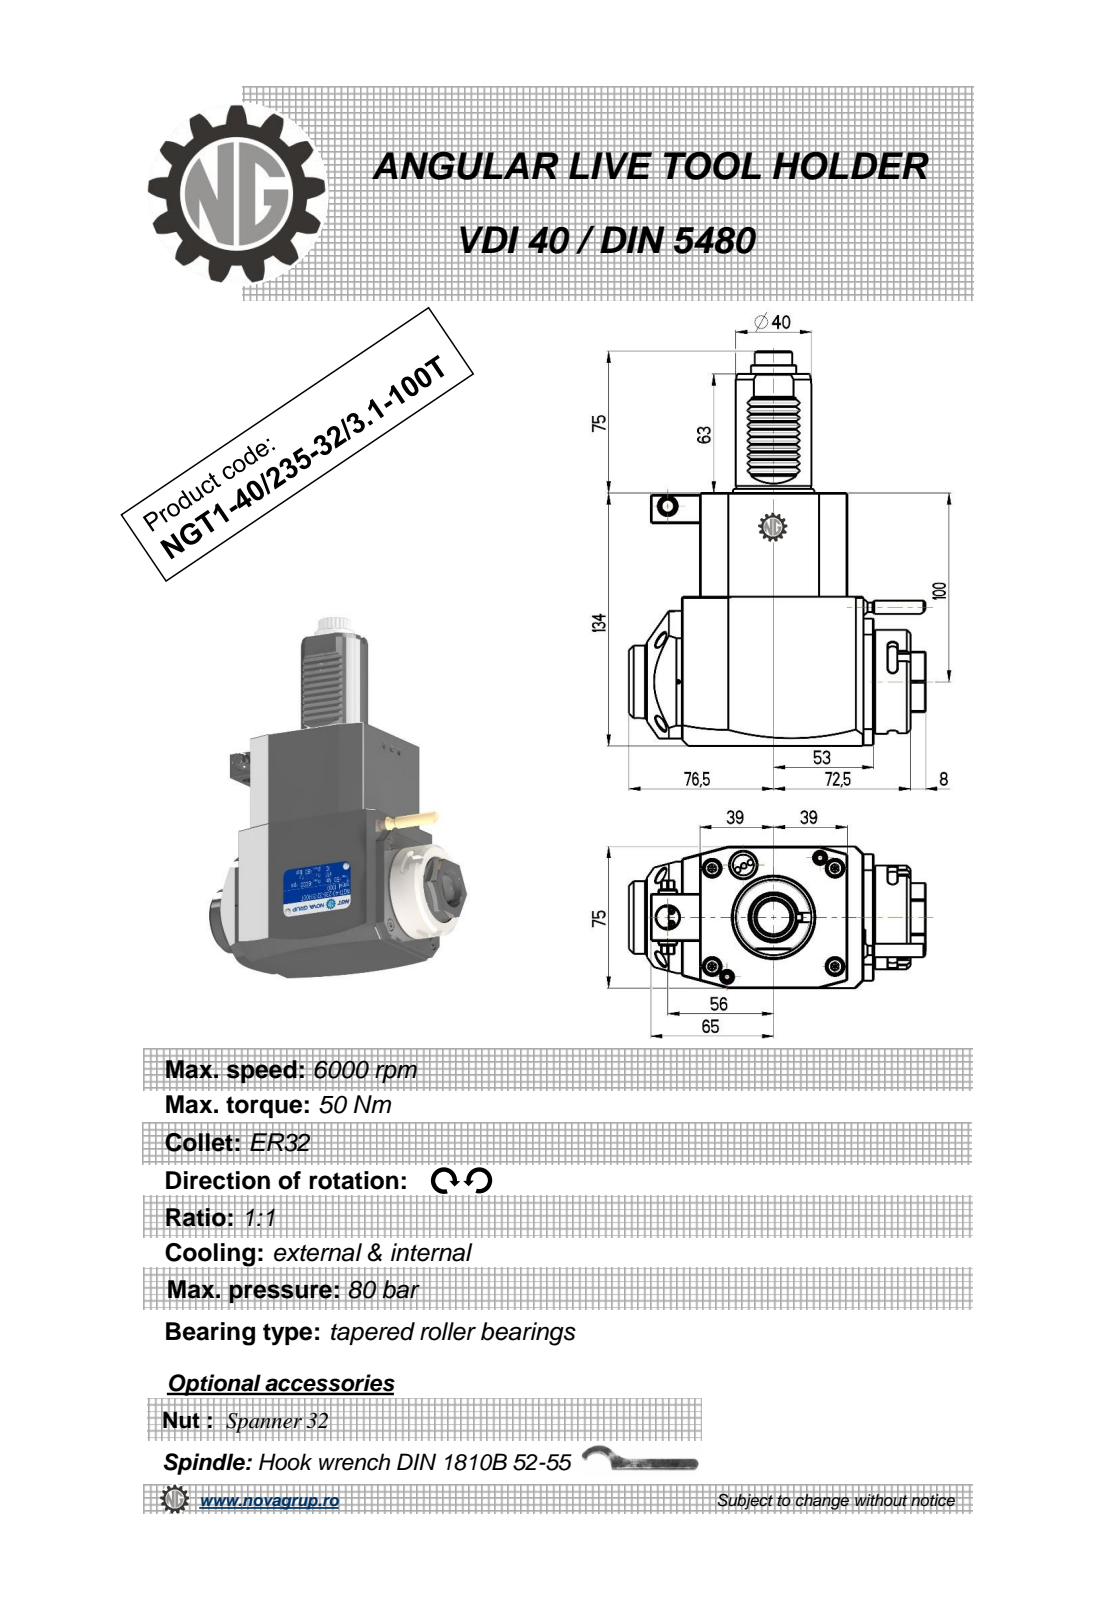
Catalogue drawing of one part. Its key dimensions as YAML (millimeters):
part_name: "NGT1_40_235_32_3_1_100T"
step_written_by: "PRO/ENGINEER BY PARAMETRIC TECHNOLOGY CORPORATION, 2010280 (CONFIG_CONTROL_DESIGN)"
units: millimeters
bodies: {solids: 1, faces: 462, planar: 192, cylindrical: 174, other: 96}
overall_size: [209, 157, 75]
volume: 1091000
surface_area: 78751
round_holes:
  - {diameter: 2.5, count: 1}
  - {diameter: 3, count: 1}
  - {diameter: 9.5, count: 1}
  - {diameter: 12, count: 1}
  - {diameter: 23, count: 1}
round_bosses_or_shafts:
  - {diameter: 8, count: 2}
  - {diameter: 55, count: 1}
  - {diameter: 48, count: 1}
  - {diameter: 40, count: 1}
  - {diameter: 38.5, count: 1}
  - {diameter: 24, count: 1}
  - {diameter: 10, count: 1}
  - {diameter: 7, count: 1}
partial_cylinders:
  - {radius: 2.08, count: 48}
  - {radius: 0.3, count: 10}
  - {radius: 2.5, count: 6}
  - {radius: 180, count: 2}
  - {radius: 3.85, count: 1}
  - {radius: 4.25, count: 1}
  - {radius: 9.08, count: 1}
  - {radius: 9.92, count: 1}
face_to_face_distances: [75, 134, 78, 14, 92, 79, 25, 84.88, 19.5, 111.5]
hole_center_spacings: [43.2, 54.87, 91.5]
